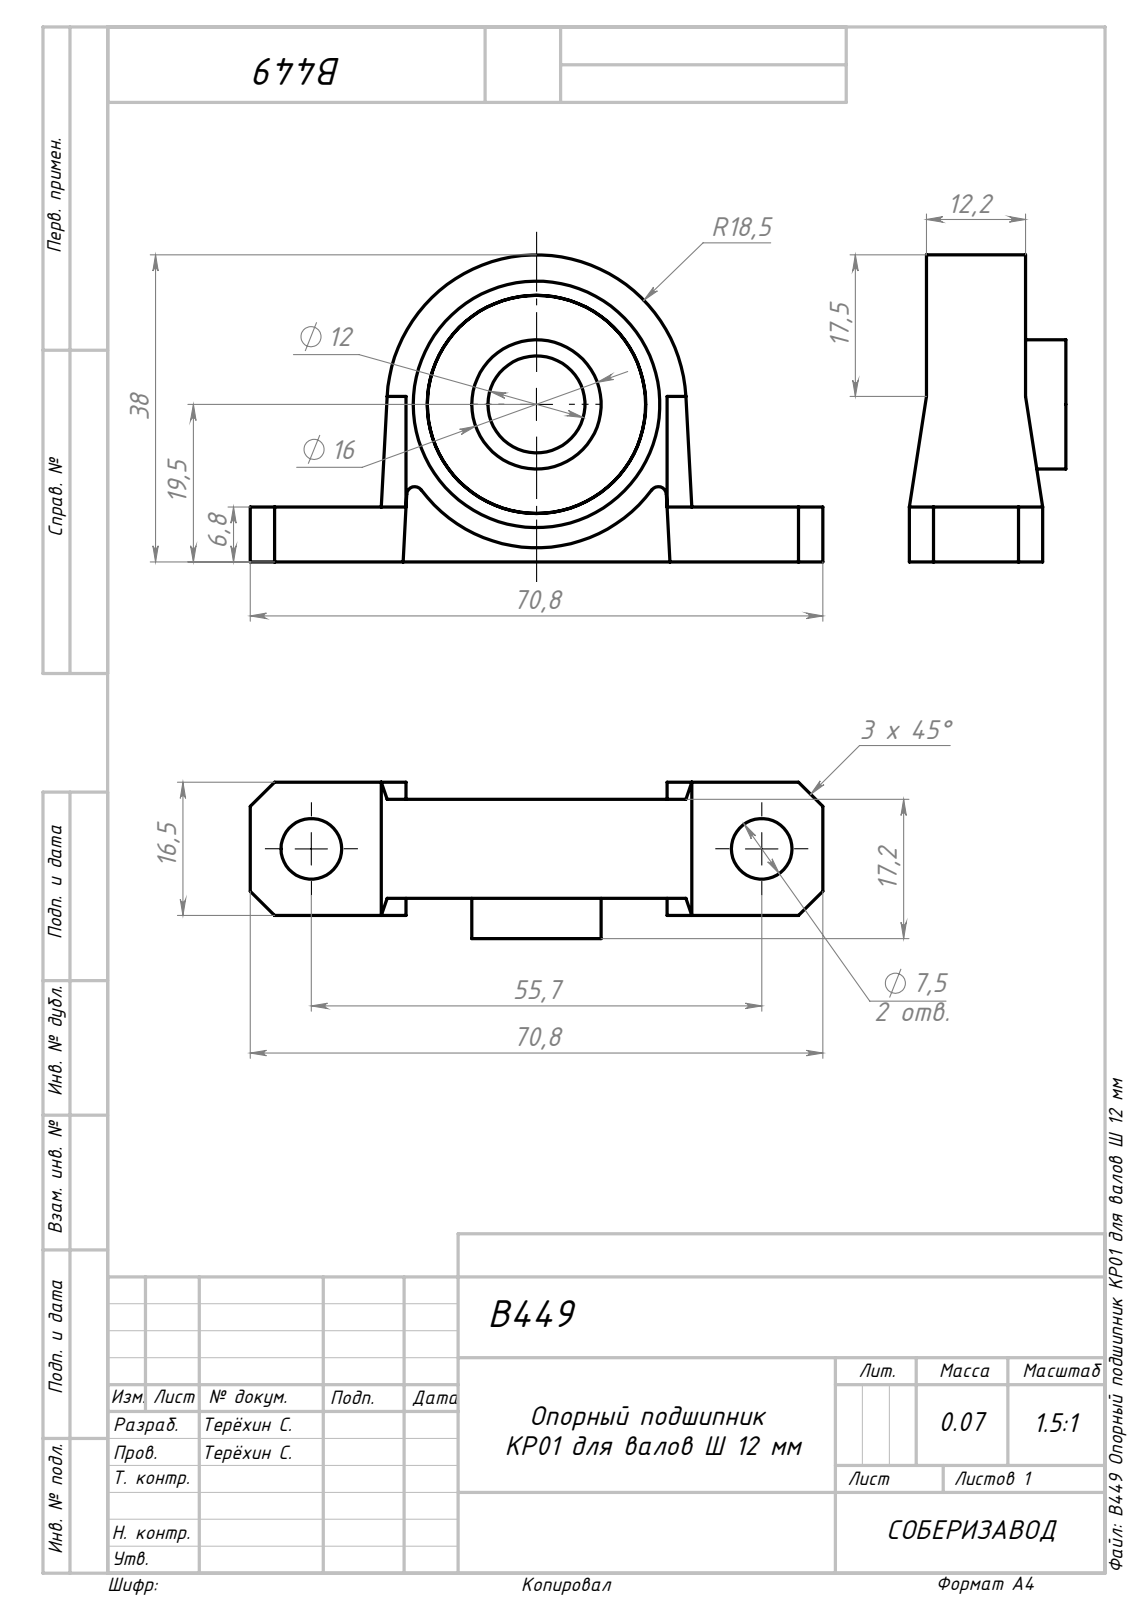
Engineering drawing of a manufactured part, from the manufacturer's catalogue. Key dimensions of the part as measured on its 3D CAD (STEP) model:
Part name (STEP PRODUCT): Сборка3; B449 Опорный подшипник KP01 для валов Ø 12 мм_00
STEP written by: SolidWorks 2024 (AUTOMOTIVE_DESIGN)
Units: millimetres
Bodies: 3 solids, 62 faces (37 planar, 25 cylindrical, 0 other)
Overall size (bounding box): 70.8 × 38 × 19.35
Volume: 14 882 mm³ · Surface area: 9 404 mm²
Round holes (diameter × count): ⌀7.5 ×2, ⌀12 ×1, ⌀16 ×1, ⌀27 ×1, ⌀30.5 ×1
Partial cylindrical surfaces — rounded edges, fillets, slot ends (radius × count): R1 ×2, R17.75 ×1, R18.5 ×1
Main face-to-face distances: 12.25, 8, 2.12, 2.13, 4.25, 6.8, 10.12, 10.13, 14.37, 16.5
Hole centre spacings: 55.7
